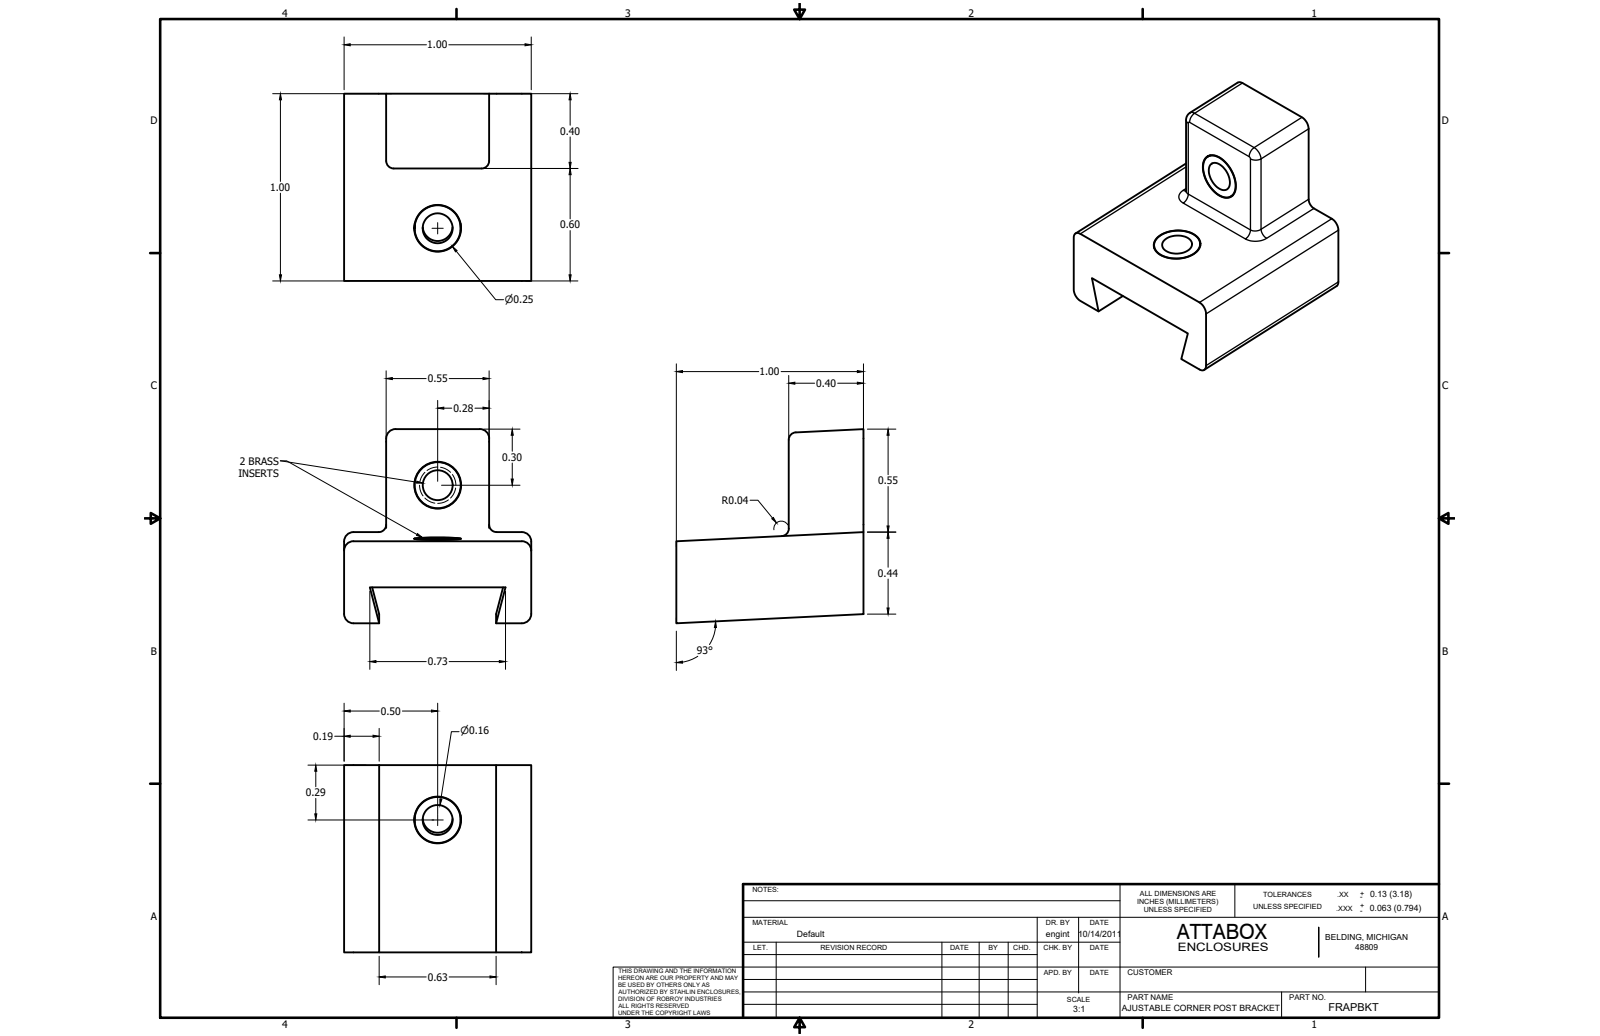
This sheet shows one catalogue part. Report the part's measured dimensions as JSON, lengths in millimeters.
{"part_name": "FRAPBKT", "step_written_by": "SolidWorks 2019 (AUTOMOTIVE_DESIGN)", "units": "millimeters", "bodies": {"solids": 12, "faces": 248, "planar": 112, "cylindrical": 76, "other": 60}, "overall_size": [152.7, 152.7, 30.8], "volume_mm3": 30920, "surface_area_mm2": 17180, "round_holes": [[6.4, 8]], "round_bosses_or_shafts": [[4.8, 8], [9.5, 4], [8, 4]], "partial_cylinders_radius": [[1.5, 40], [0.3, 12]], "face_to_face_distances": [6.4, 172.8, 81.7, 179.2, 87.5, 5.8, 25.4, 166.4, 20.6, 158.5], "hole_center_spacings": [108, 152.8]}
